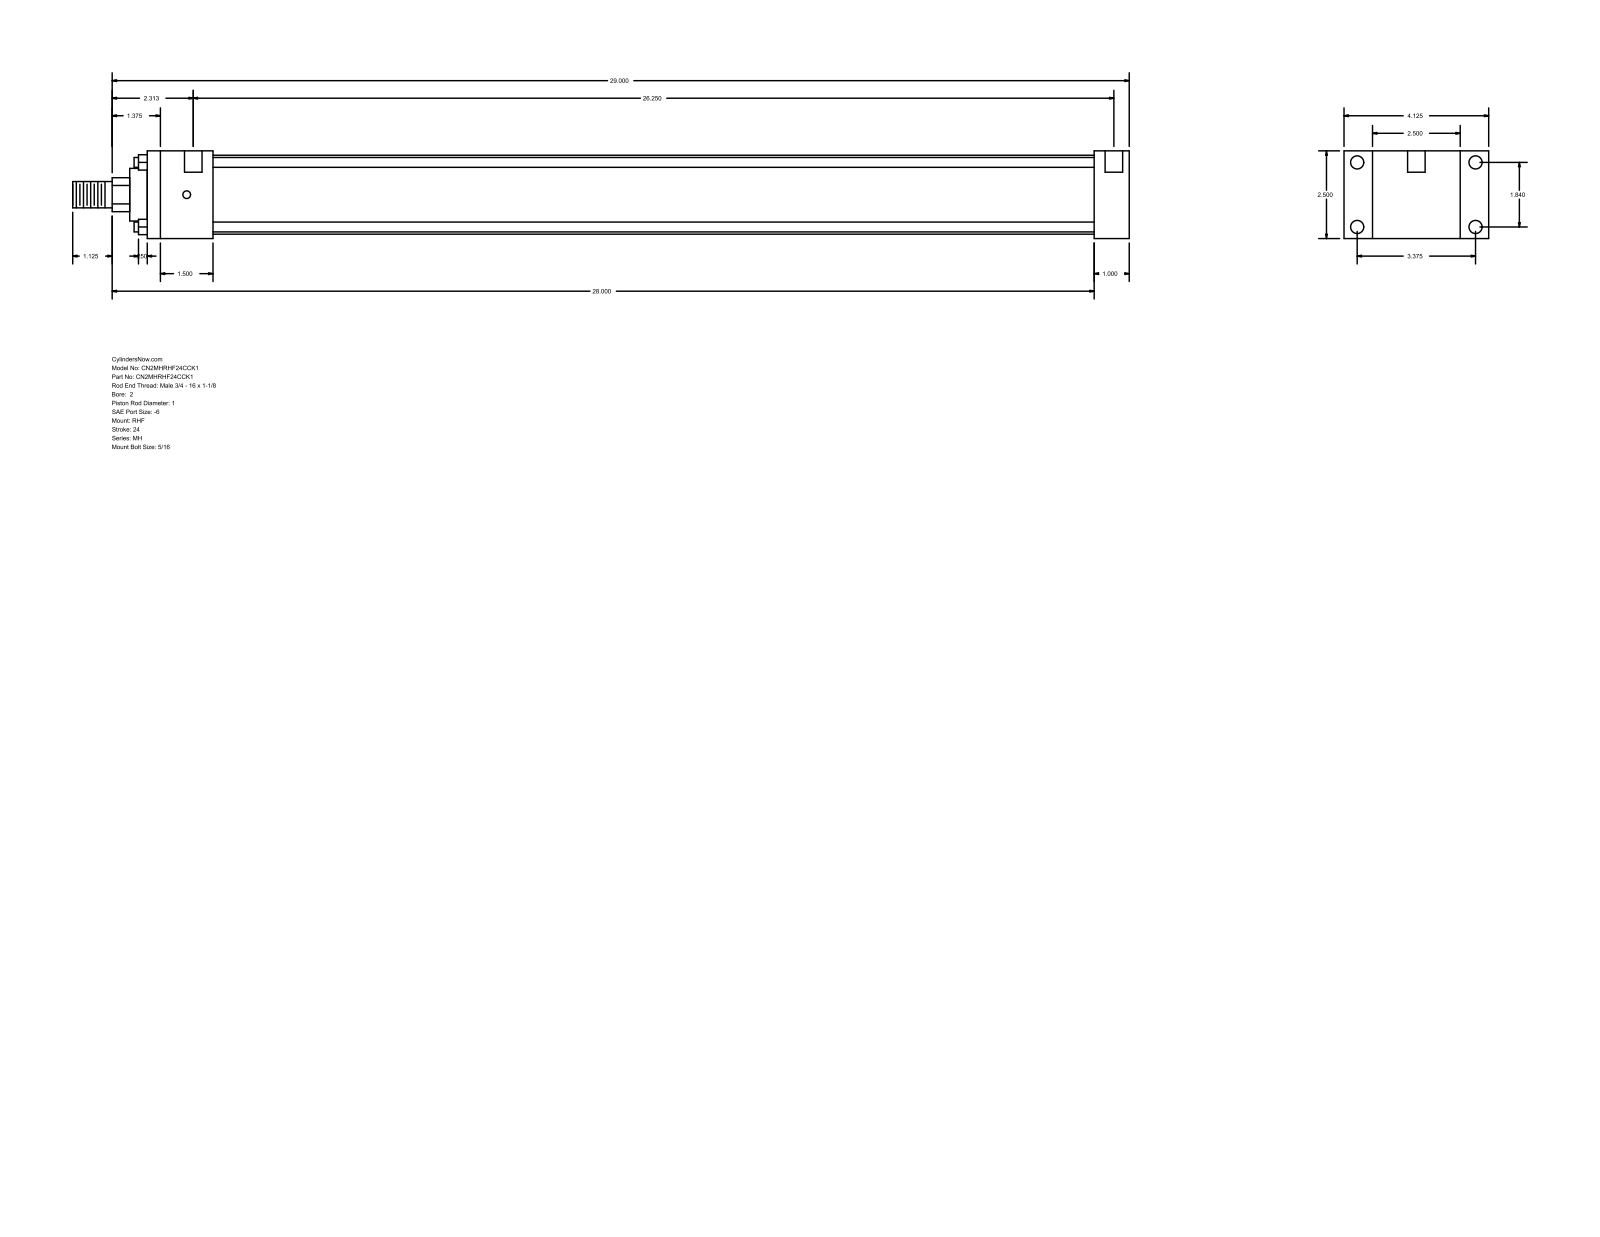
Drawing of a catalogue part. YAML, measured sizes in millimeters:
part_name: "MH_RHF__0200_1"
step_written_by: "GSSL Pune (CONFIG_CONTROL_DESIGN)"
units: millimeters
bodies: {solids: 0, faces: 88, planar: 60, cylindrical: 28, other: 0}
overall_size: [765.17, 104.78, 63.5]
round_holes:
  - {diameter: 5.56, count: 4}
  - {diameter: 9.53, count: 4}
  - {diameter: 12.7, count: 2}
round_bosses_or_shafts:
  - {diameter: 7.14, count: 4}
  - {diameter: 57.15, count: 1}
  - {diameter: 38.1, count: 1}
  - {diameter: 25.4, count: 1}
  - {diameter: 19.05, count: 1}
partial_cylinders:
  - {radius: 12.29, count: 1}
face_to_face_distances: [63.5, 25.4, 20.64, 84.14, 711.2, 685.8, 104.78, 47.63, 638.17, 663.57]
hole_center_spacings: [46.74, 85.72, 97.63, 674.68, 3.17, 4.76, 666.75, 669.92]
